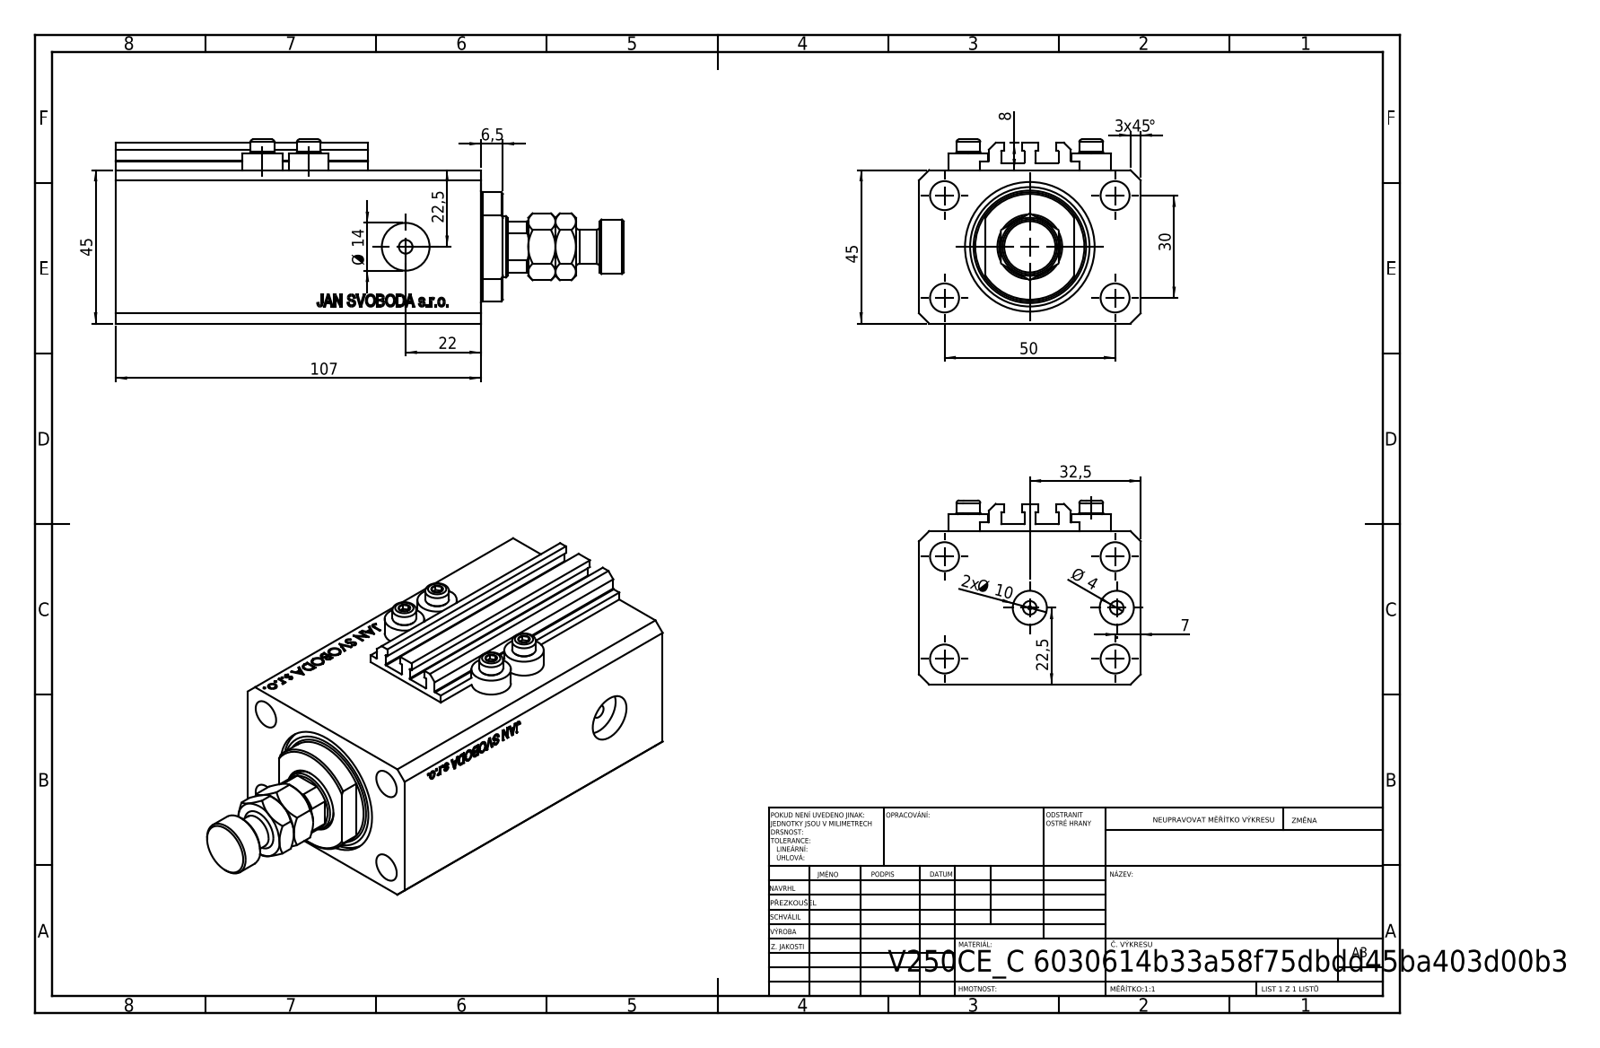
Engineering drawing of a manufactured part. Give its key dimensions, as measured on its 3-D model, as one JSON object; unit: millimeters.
{"part_name": "ALLEN BOLT V250CE; MFA; V250CE_C_VCP; V250CE_VC_C (+1 more)", "step_written_by": "SolidWorks 2019 (CONFIG_CONTROL_DESIGN)", "units": "millimeters", "bodies": {"solids": 9, "faces": 1090, "planar": 520, "cylindrical": 92, "other": 478}, "overall_size": [148.9, 65, 54], "volume_mm3": 294034, "surface_area_mm2": 78553, "round_holes": [[4, 8], [8.5, 5], [10, 2], [14, 2], [1.25, 1], [18, 1], [25, 1], [38, 1]], "round_bosses_or_shafts": [[11.6, 4], [7, 4], [16, 1]], "partial_cylinders_radius": [[0.2, 10], [8.5, 1], [16, 1]], "face_to_face_distances": [45, 65, 107, 81.9, 25.1, 47, 6.9, 2.5, 6, 10], "hole_center_spacings": [29.15, 13.6, 15.01, 30, 36, 38.48, 50, 52.68]}
